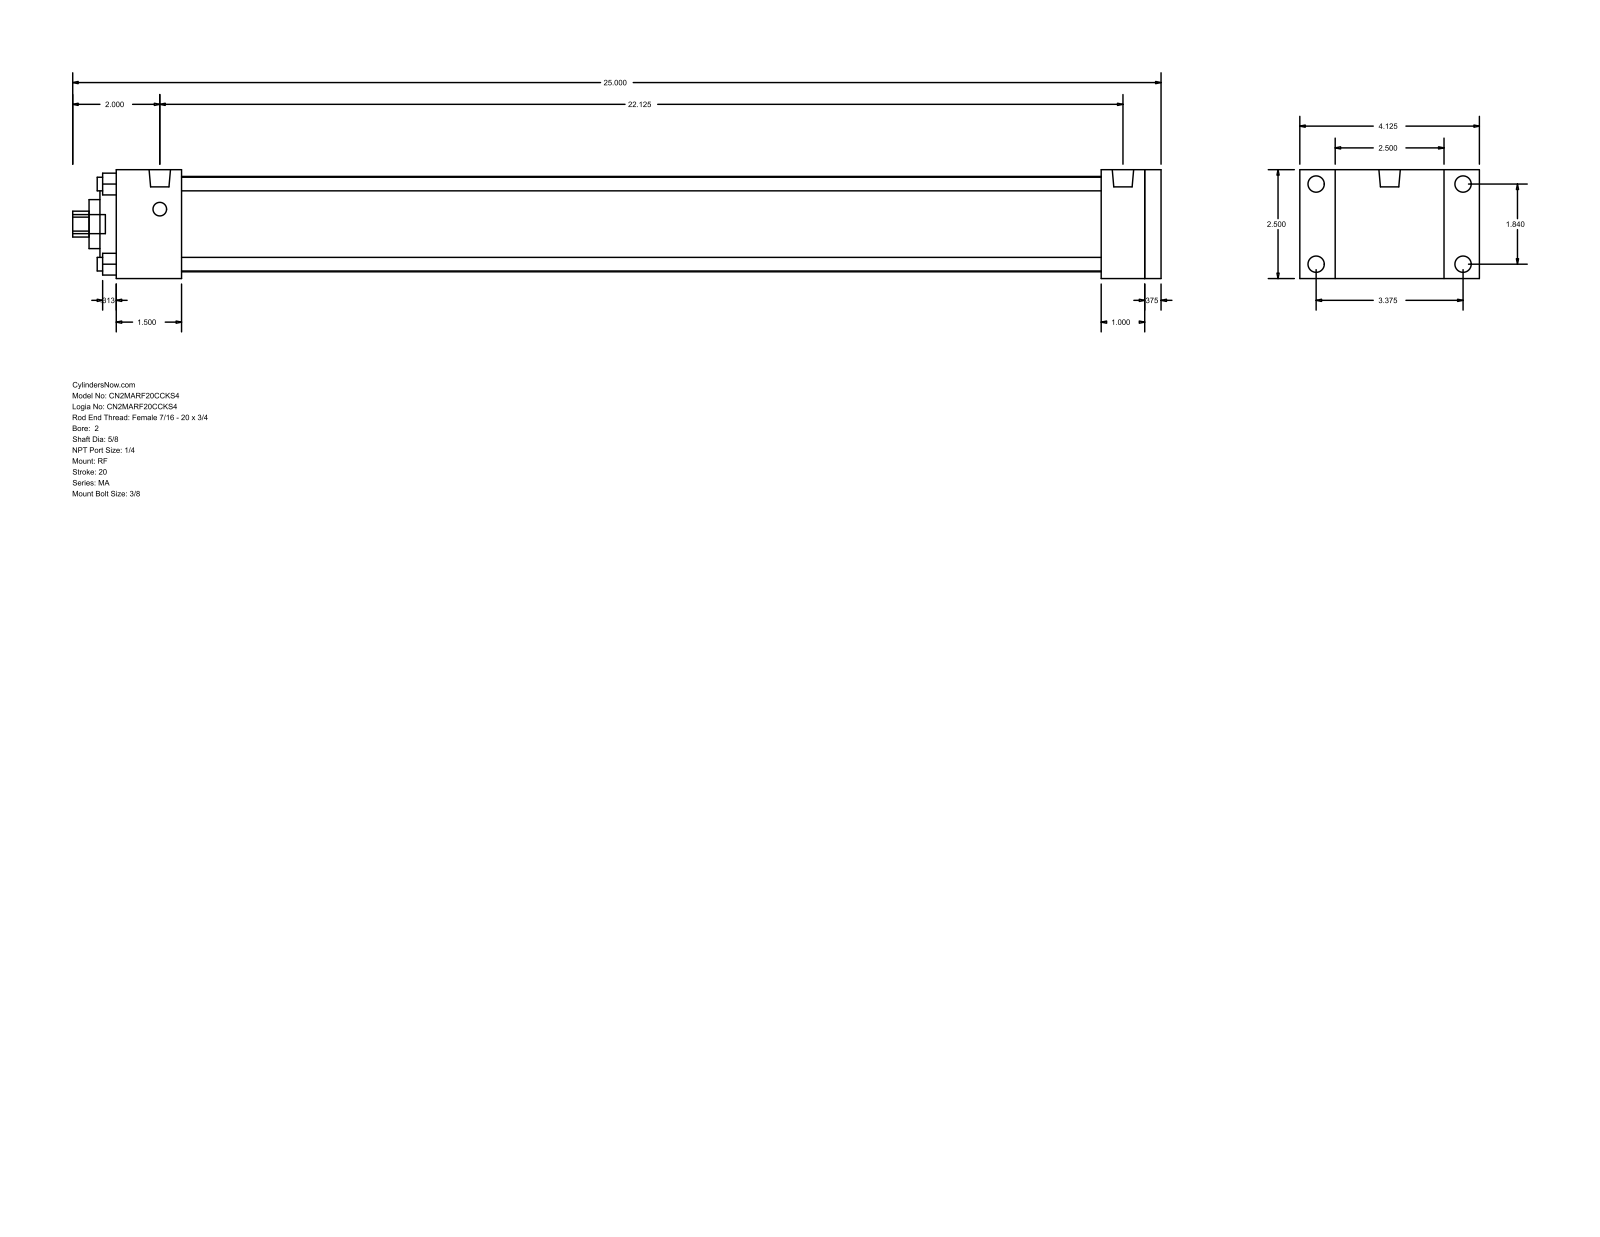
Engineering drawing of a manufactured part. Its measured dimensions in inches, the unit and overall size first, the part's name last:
Units: inches
Overall size (bounding box): 25 × 4.125 × 2.5
Round holes (diameter × count): ⌀0.313 ×4, ⌀0.625 ×1, ⌀1.125 ×1, ⌀2 ×1, ⌀2.19 ×1
Round bosses / shafts (diameter × count): ⌀0.375 ×4, ⌀0.313 ×4, ⌀0.492 ×2, ⌀0.437 ×1
Partial cylindrical surfaces — rounded edges, fillets, slot ends (radius × count): R0.297 ×1
Main face-to-face distances: 2.5, 0.375, 24, 1, 1.5, 23.625, 22.125, 22.5, 22.625, 21.125
Hole centre spacings: 1.301, 1.84, 2.602
Bodies: 0 solids, 94 faces (65 planar, 29 cylindrical, 0 other)
Part name (STEP PRODUCT): MA_RF__0200_0.625
STEP written by: GSSL Pune (CONFIG_CONTROL_DESIGN)
